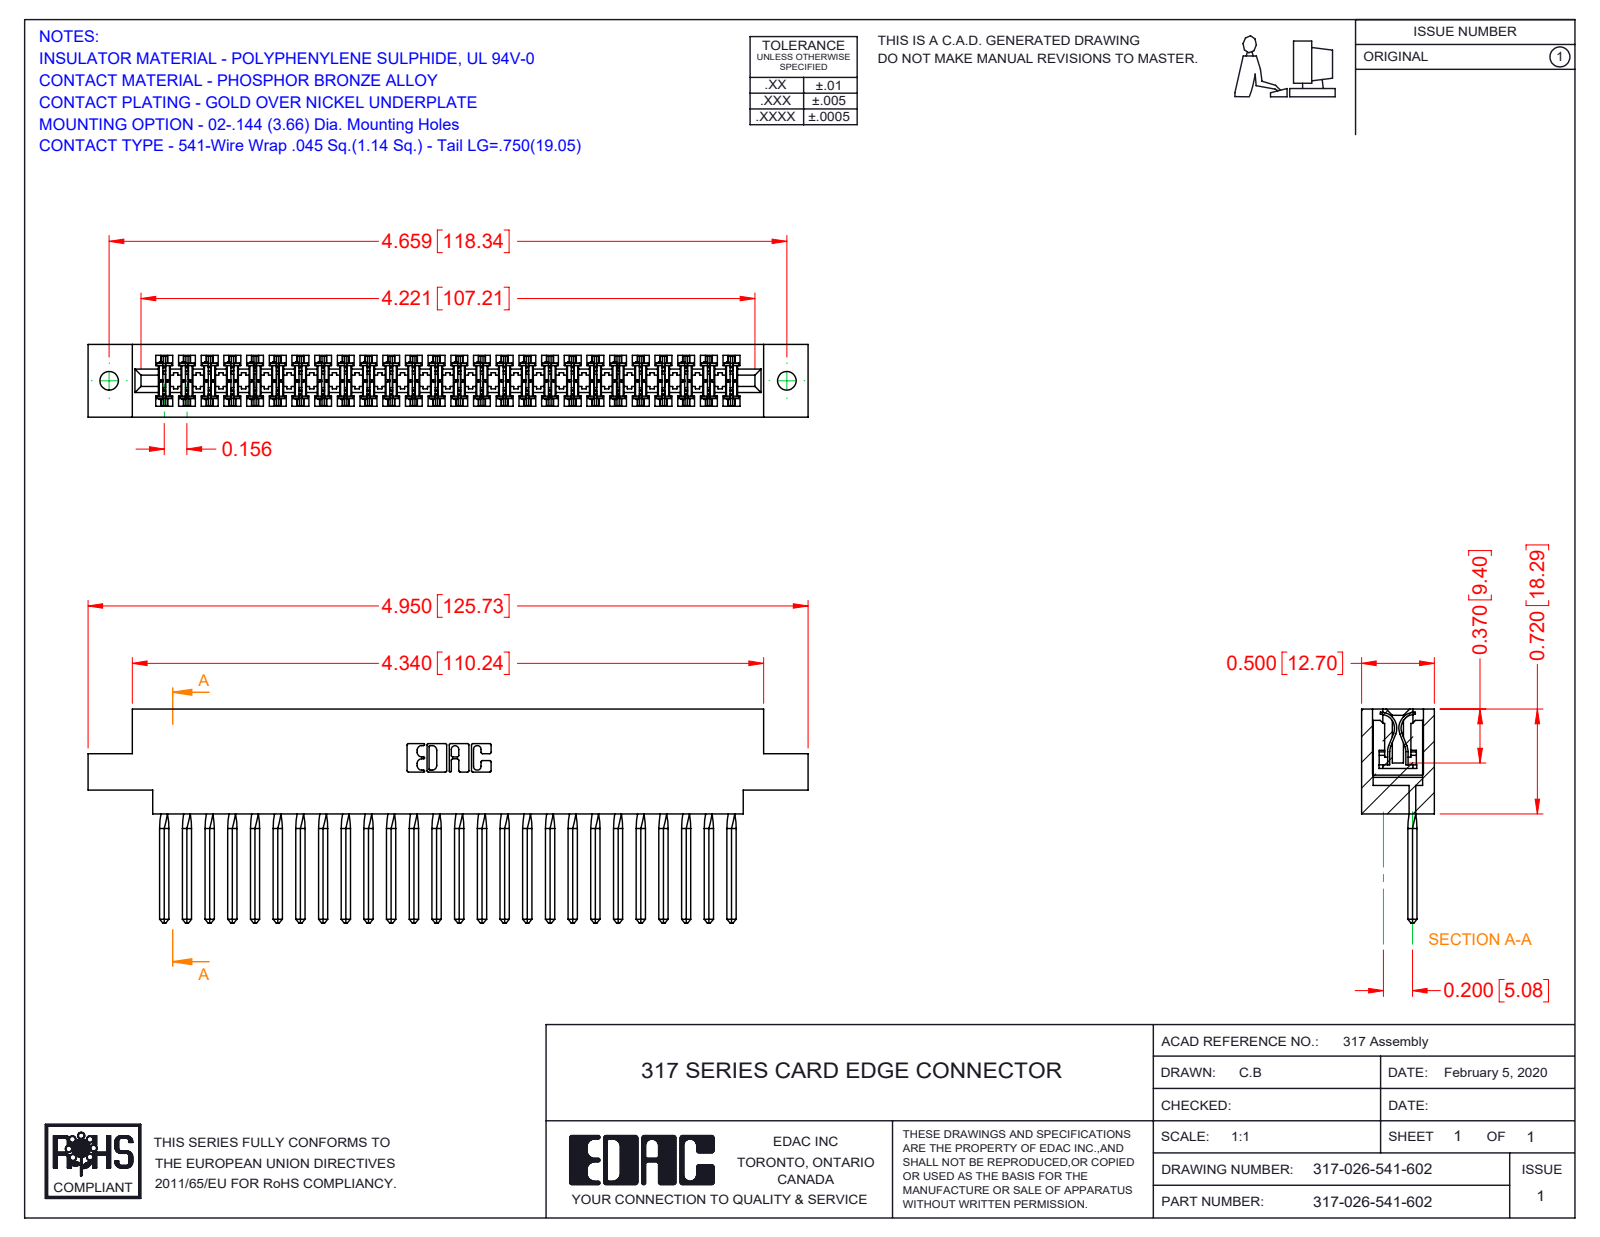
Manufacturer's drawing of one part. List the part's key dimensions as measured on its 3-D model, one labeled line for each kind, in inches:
Part name (STEP PRODUCT): 317-290-002_541; 317 Part_.144 Dia; 317-026-541-602
STEP written by: SolidWorks 2016 (CONFIG_CONTROL_DESIGN)
Units: inches
Bodies: 27 solids, 4054 faces (3282 planar, 668 cylindrical, 104 other)
Overall size (bounding box): 4.95 × 1.47 × 0.5
Volume: 1.212 in³ · Surface area: 42.26 in²
Round holes (diameter × count): ⌀0.128 ×2
Partial cylindrical surfaces — rounded edges, fillets, slot ends (radius × count): R0.015 ×52, R0.01 ×22, R0.007 ×6, R0.031 ×6, R0.026 ×3, R0.095 ×2, R0.1 ×2, R0.11 ×2
Main face-to-face distances: 0.5, 0.075, 0.425, 0.35, 0.11, 0.195, 0.72, 0.772, 0.211, 0.289
Hole centre spacings: 4.659
